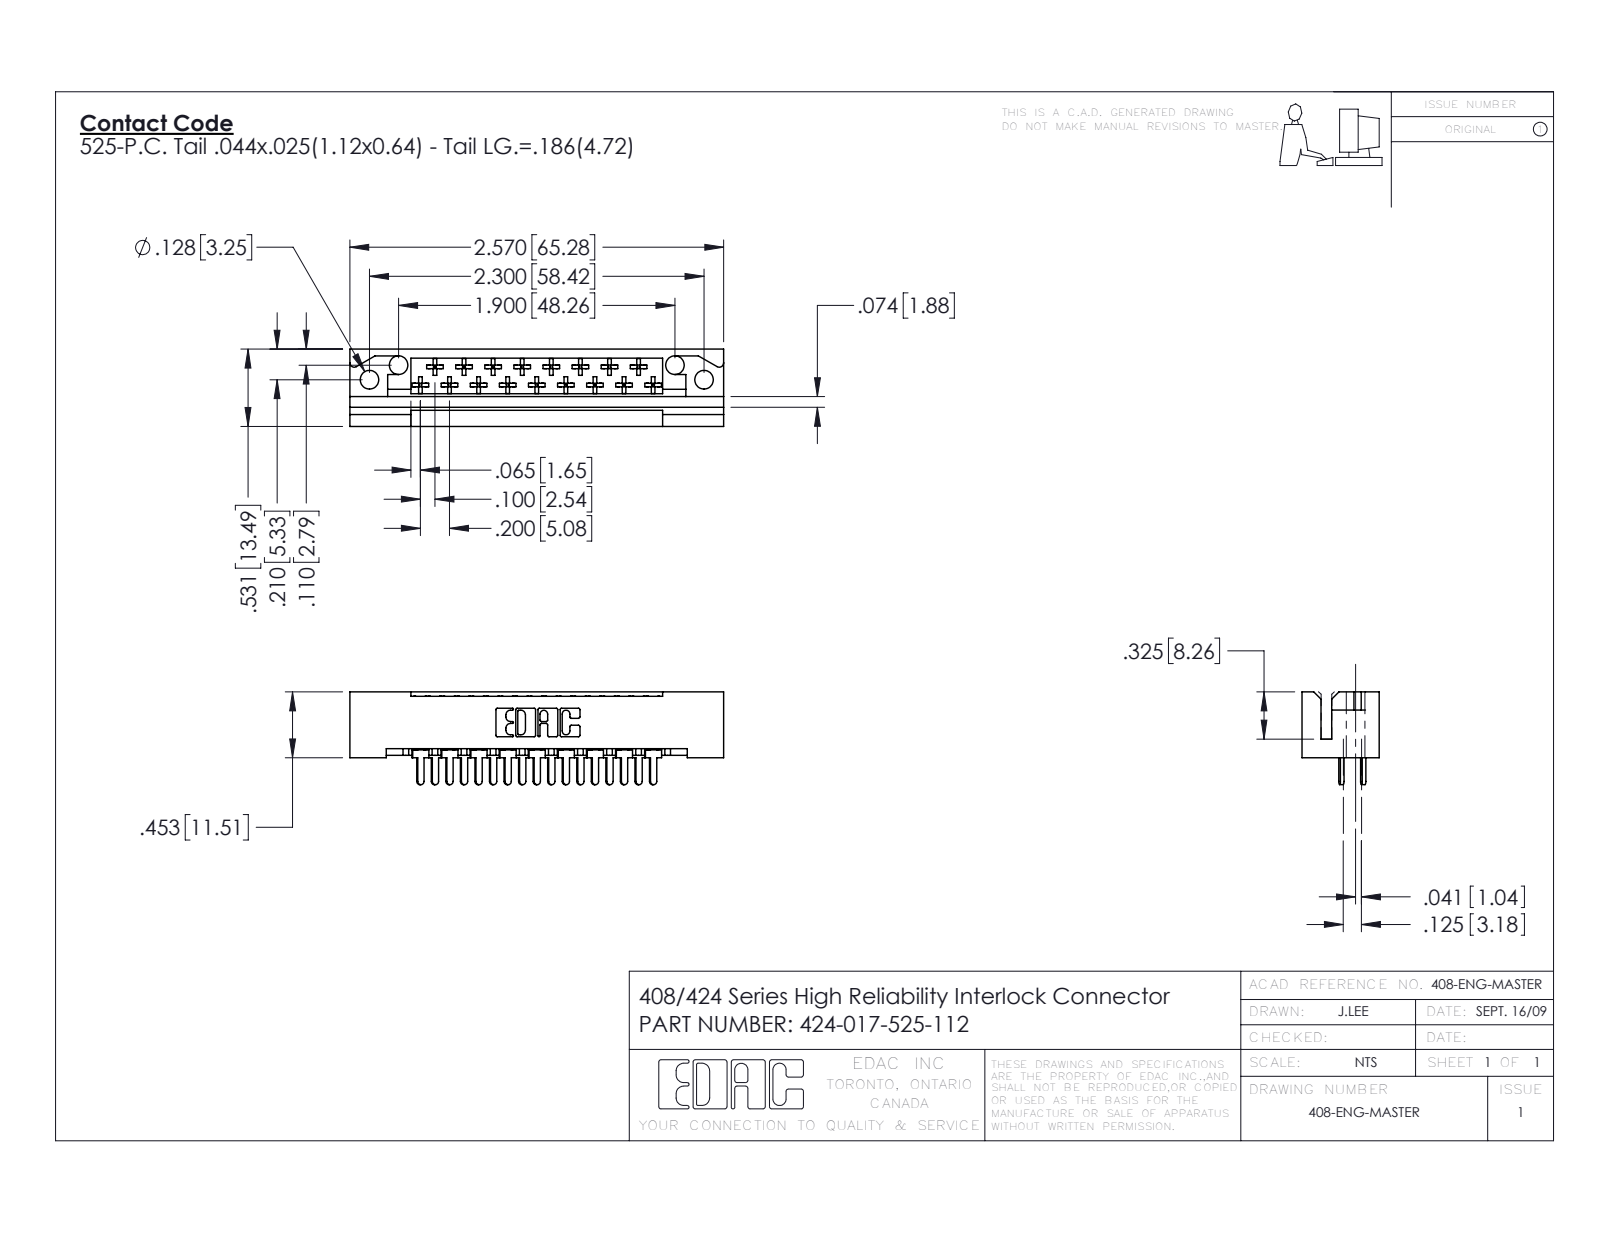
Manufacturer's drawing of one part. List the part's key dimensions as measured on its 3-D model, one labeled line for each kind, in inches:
Part name (STEP PRODUCT): 424-017-525-112; 408-290-001_408-290-125 - Top; 408-290-001_408-290-125 - Bottom; 424 Part_017
STEP written by: SolidWorks 2016 (CONFIG_CONTROL_DESIGN)
Units: inches
Bodies: 18 solids, 1080 faces (803 planar, 209 cylindrical, 68 other)
Overall size (bounding box): 2.57 × 0.638 × 0.531
Volume: 0.432 in³ · Surface area: 13.07 in²
Round holes (diameter × count): ⌀0.128 ×4
Partial cylindrical surfaces — rounded edges, fillets, slot ends (radius × count): R0.01 ×102, R0.01 ×22, R0.02 ×19, R0.022 ×17, R0.007 ×6, R0.031 ×6, R0.026 ×3, R0.03 ×2
Main face-to-face distances: 0.4, 0.025, 0.531, 0.125, 0.1, 0.131, 0.326, 0.074, 0.205, 0.025
Hole centre spacings: 0.224, 2.102, 1.9, 2.3
